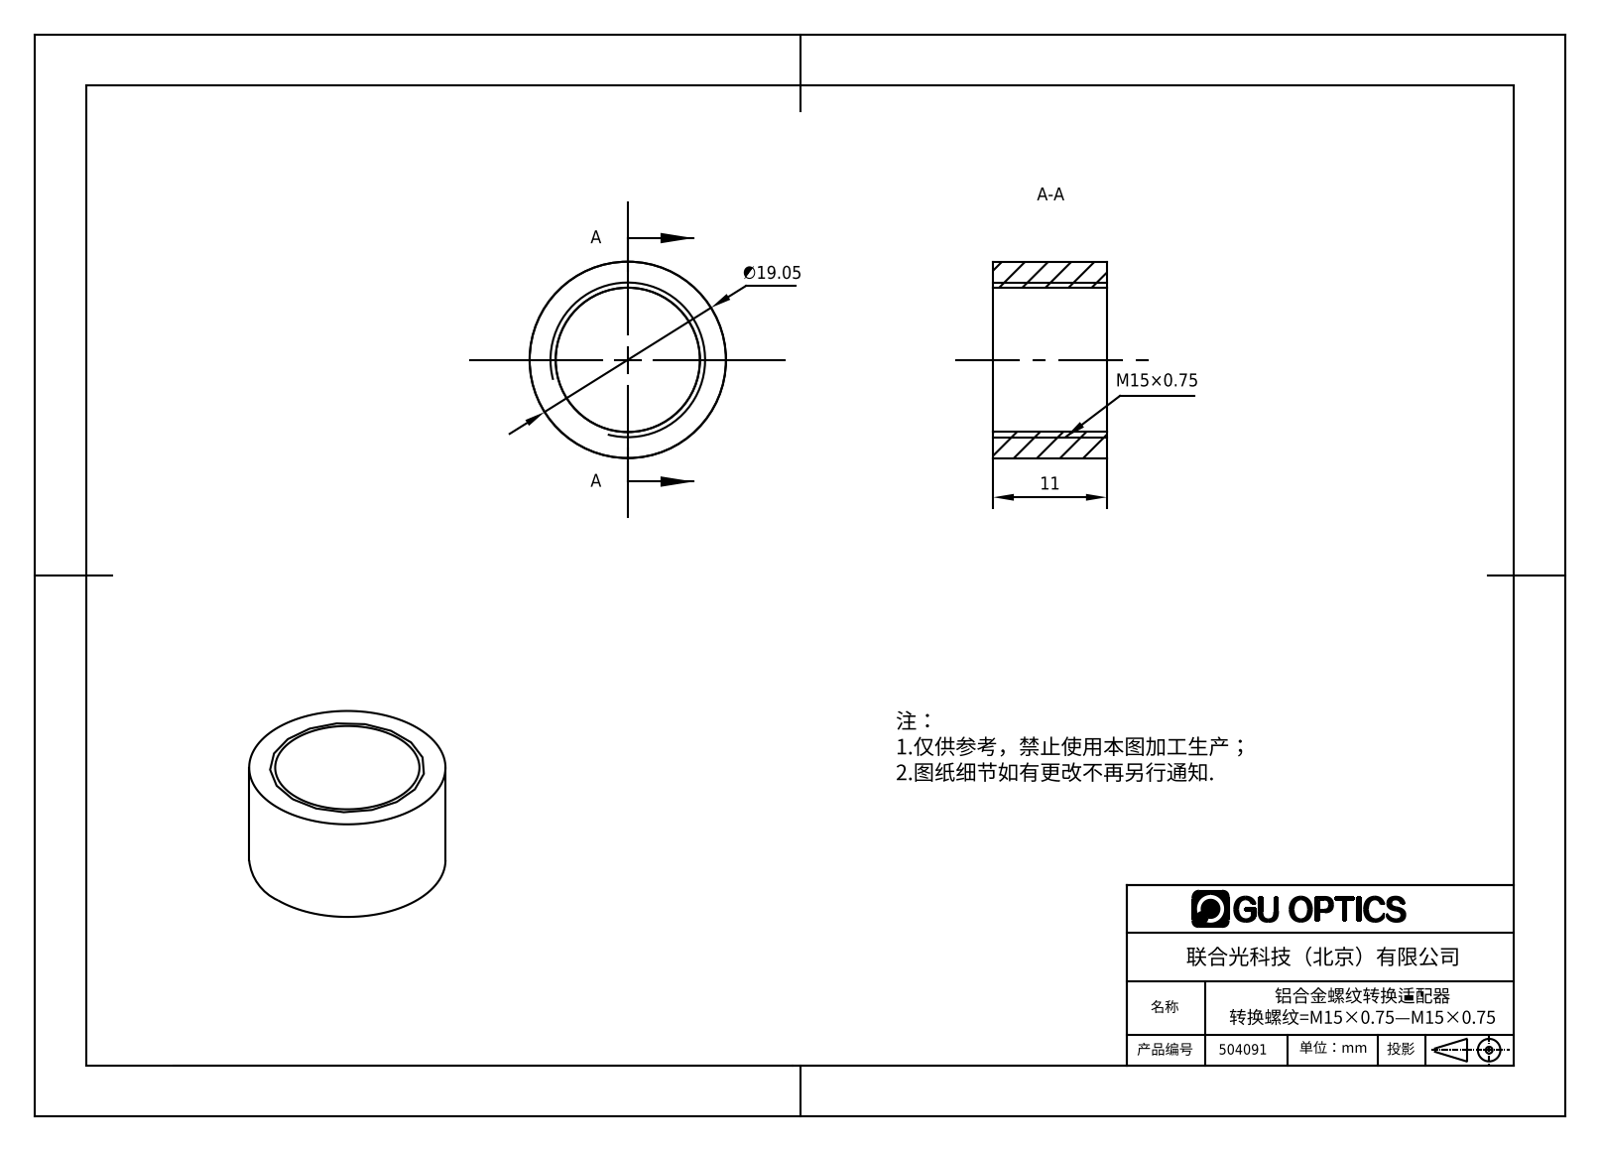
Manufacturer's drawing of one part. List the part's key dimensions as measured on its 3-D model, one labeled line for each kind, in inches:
Part name (STEP PRODUCT): 504091
STEP written by: SolidWorks 2016 (AUTOMOTIVE_DESIGN)
Units: inches
Bodies: 1 solid, 6 faces (2 planar, 4 cylindrical, 0 other)
Overall size (bounding box): 0.75 × 0.75 × 0.433
Volume: 0.088 in³ · Surface area: 2.176 in²
Round holes (diameter × count): ⌀0.551 ×1
Round bosses / shafts (diameter × count): ⌀0.75 ×1
Main face-to-face distances: 0.433
